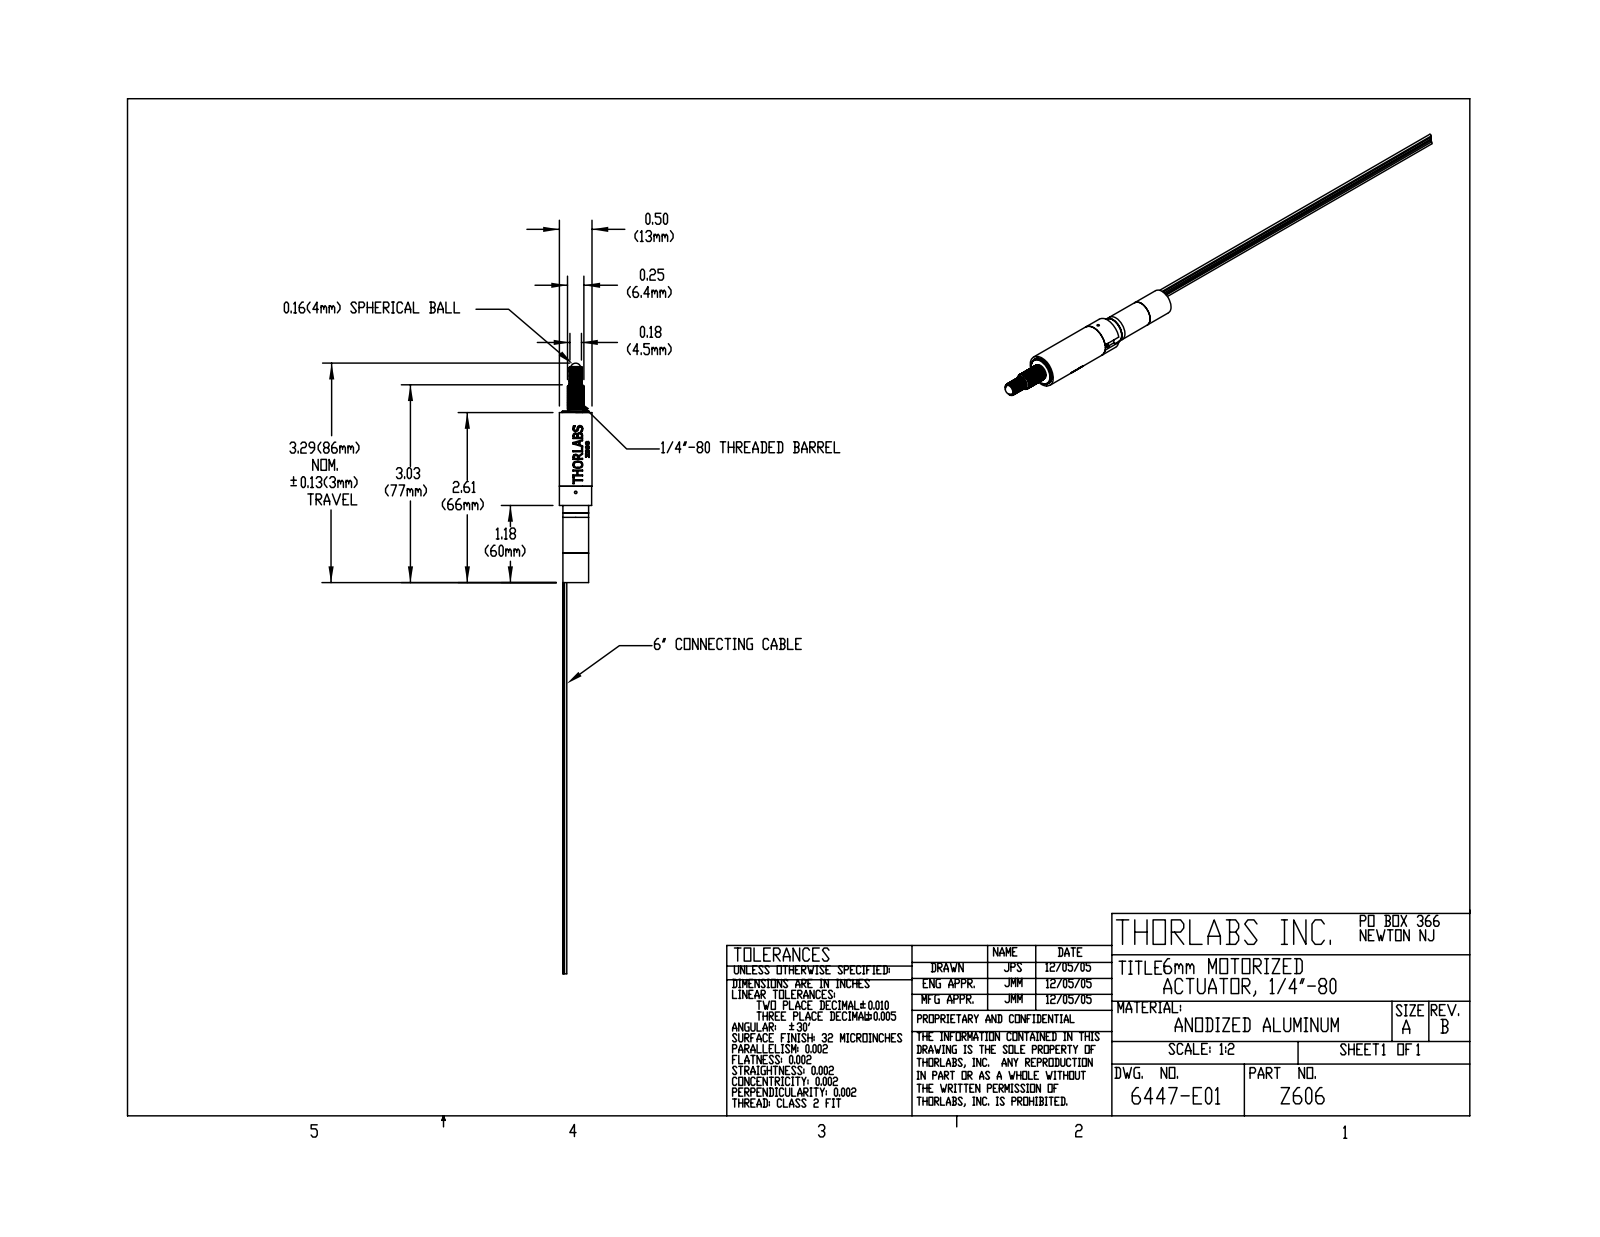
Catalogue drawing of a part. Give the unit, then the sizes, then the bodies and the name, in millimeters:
Units: millimetres
Overall size (bounding box): 237.9 × 12.7 × 12.7
Round holes (diameter × count): ⌀1 ×1, ⌀11 ×1, ⌀12.2 ×1
Round bosses / shafts (diameter × count): ⌀12.7 ×1, ⌀10.2 ×1, ⌀10 ×1, ⌀10 ×1, ⌀6.4 ×1, ⌀6.1 ×1, ⌀5 ×1
Partial cylindrical surfaces — rounded edges, fillets, slot ends (radius × count): R0.4 ×6
Main face-to-face distances: 31.6, 34.7, 11.5, 66.9, 55.4, 27.2, 15.7, 39.7, 20.1, 4.4
Bodies: 0 solids, 226 faces (18 planar, 192 cylindrical, 16 other)
Part name (STEP PRODUCT): 6447-E0W
STEP written by: SolidWorks 2007 (AUTOMOTIVE_DESIGN)
